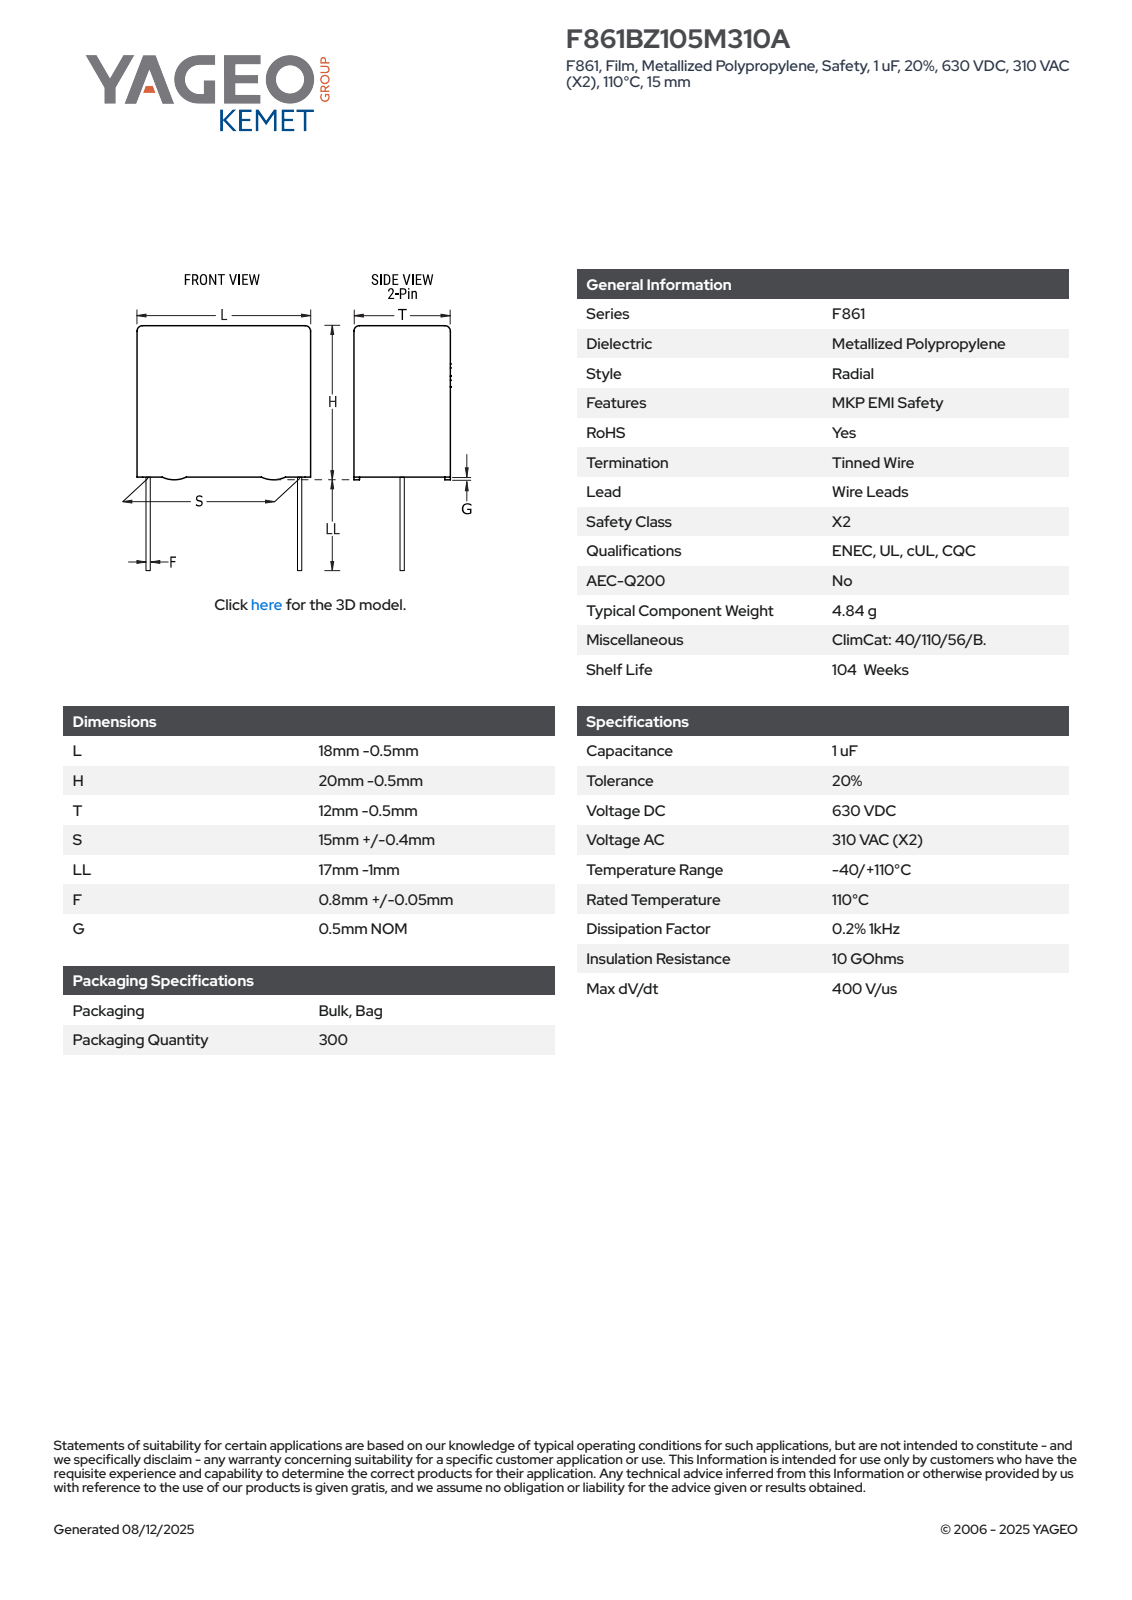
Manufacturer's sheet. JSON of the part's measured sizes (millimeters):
{"part_name": "CFR_RBG_18X20X12_L17.5H19.5T11.5S15LL16F0.85G0.5", "step_written_by": "SolidWorks 2014 (AUTOMOTIVE_DESIGN)", "units": "millimeters", "bodies": {"solids": 4, "faces": 89, "planar": 81, "cylindrical": 8, "other": 0}, "overall_size": [35.5, 17.5, 11.51], "volume_mm3": 3843, "surface_area_mm2": 1626, "round_bosses_or_shafts": [[0.85, 2]], "partial_cylinders_radius": [[0.5, 4]], "face_to_face_distances": [11.5, 17.5, 19, 0.5, 19.5, 0.66, 10.84, 10.18, 16, 16.5]}
